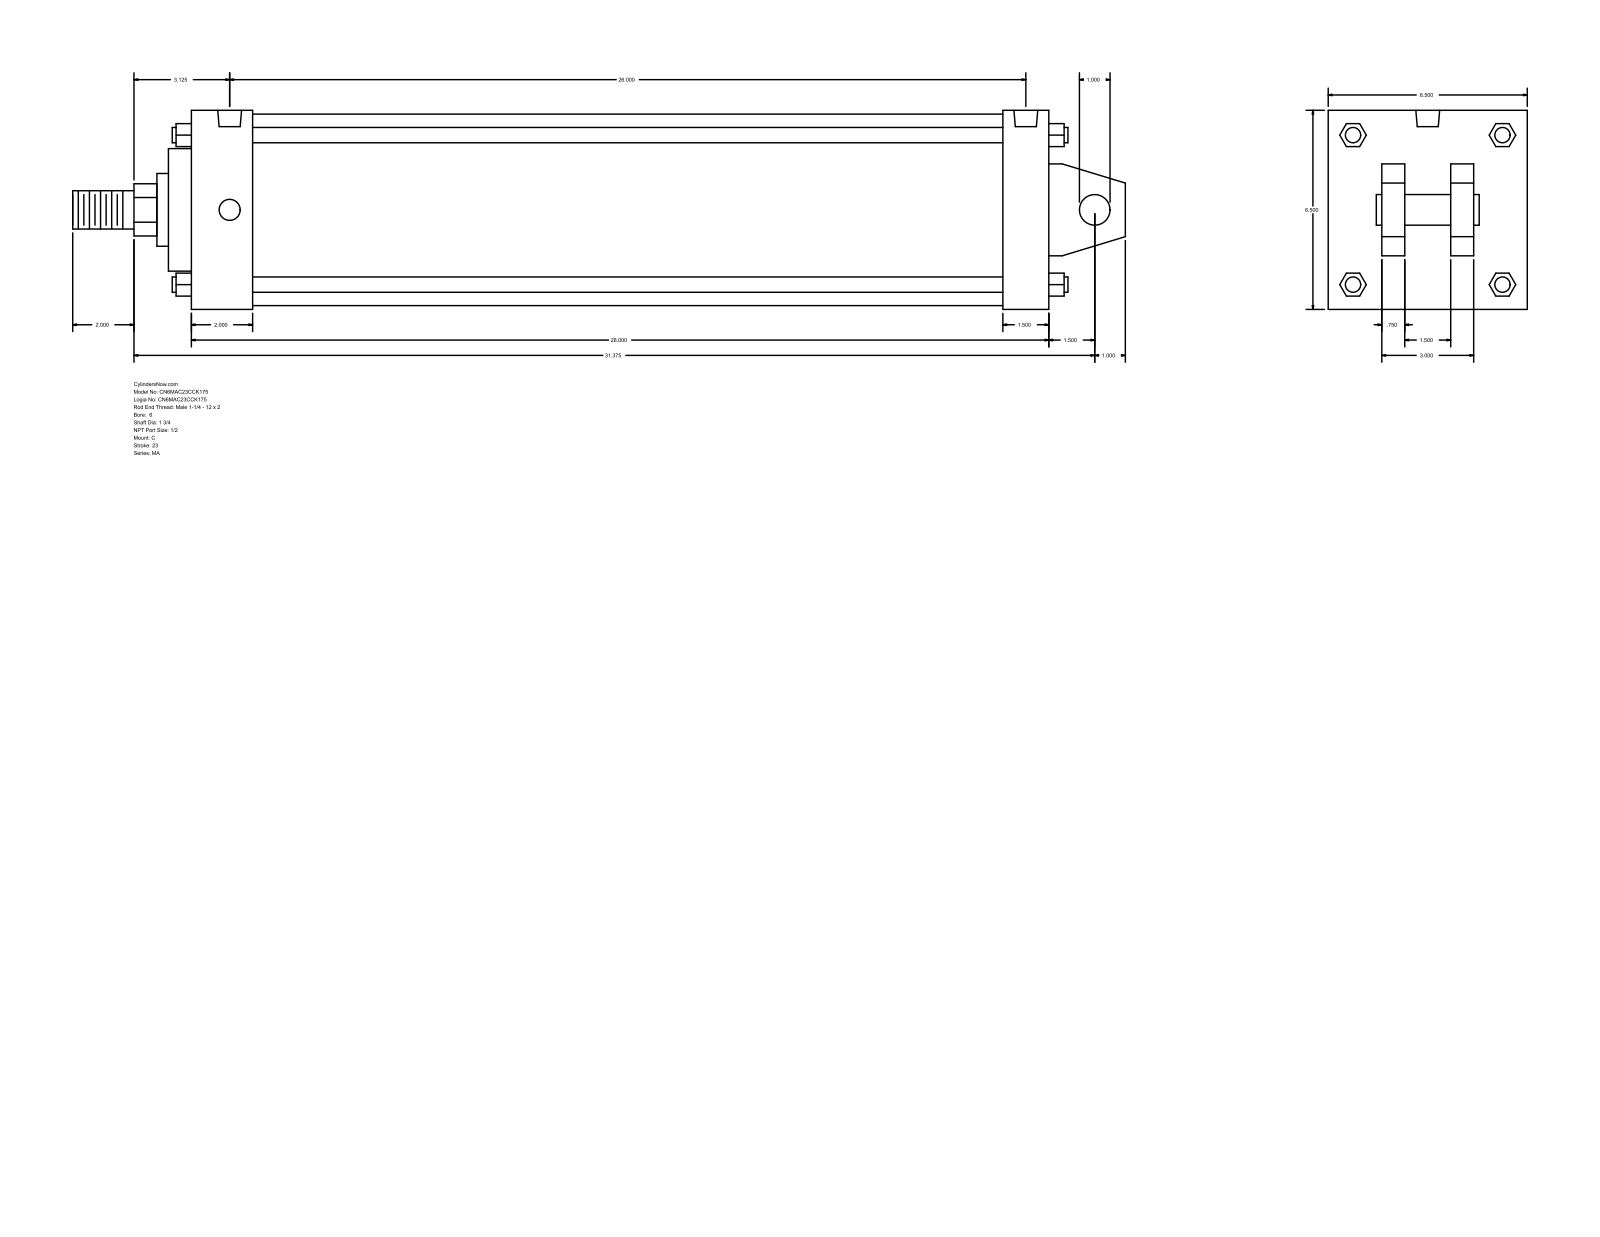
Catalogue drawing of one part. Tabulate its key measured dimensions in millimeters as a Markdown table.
| quantity | value |
| --- | --- |
| part name | MA_C__0600_1.75 |
| STEP written by | GSSL Pune (CONFIG_CONTROL_DESIGN) |
| units | millimeters |
| bodies | 0 solids, 141 faces (109 planar, 32 cylindrical, 0 other) |
| overall size | 873.12 × 165.1 × 165.1 |
| round holes (diameter × count) | 17.46 × 4, 19.77 × 2 |
| round bosses / shafts (diameter × count) | 12.7 × 4, 158.75 × 1, 101.6 × 1, 60.33 × 1, 44.45 × 1, 31.75 × 1, 25.4 × 1 |
| partial cylindrical surfaces (radius × count) | 21.63 × 1 |
| main face-to-face distances | 165.1, 711.21, 19.05, 38.1, 63.5, 101.6, 44.45, 120.65, 57.15, 50.8 |
| hole center spacings | 660.39 |
